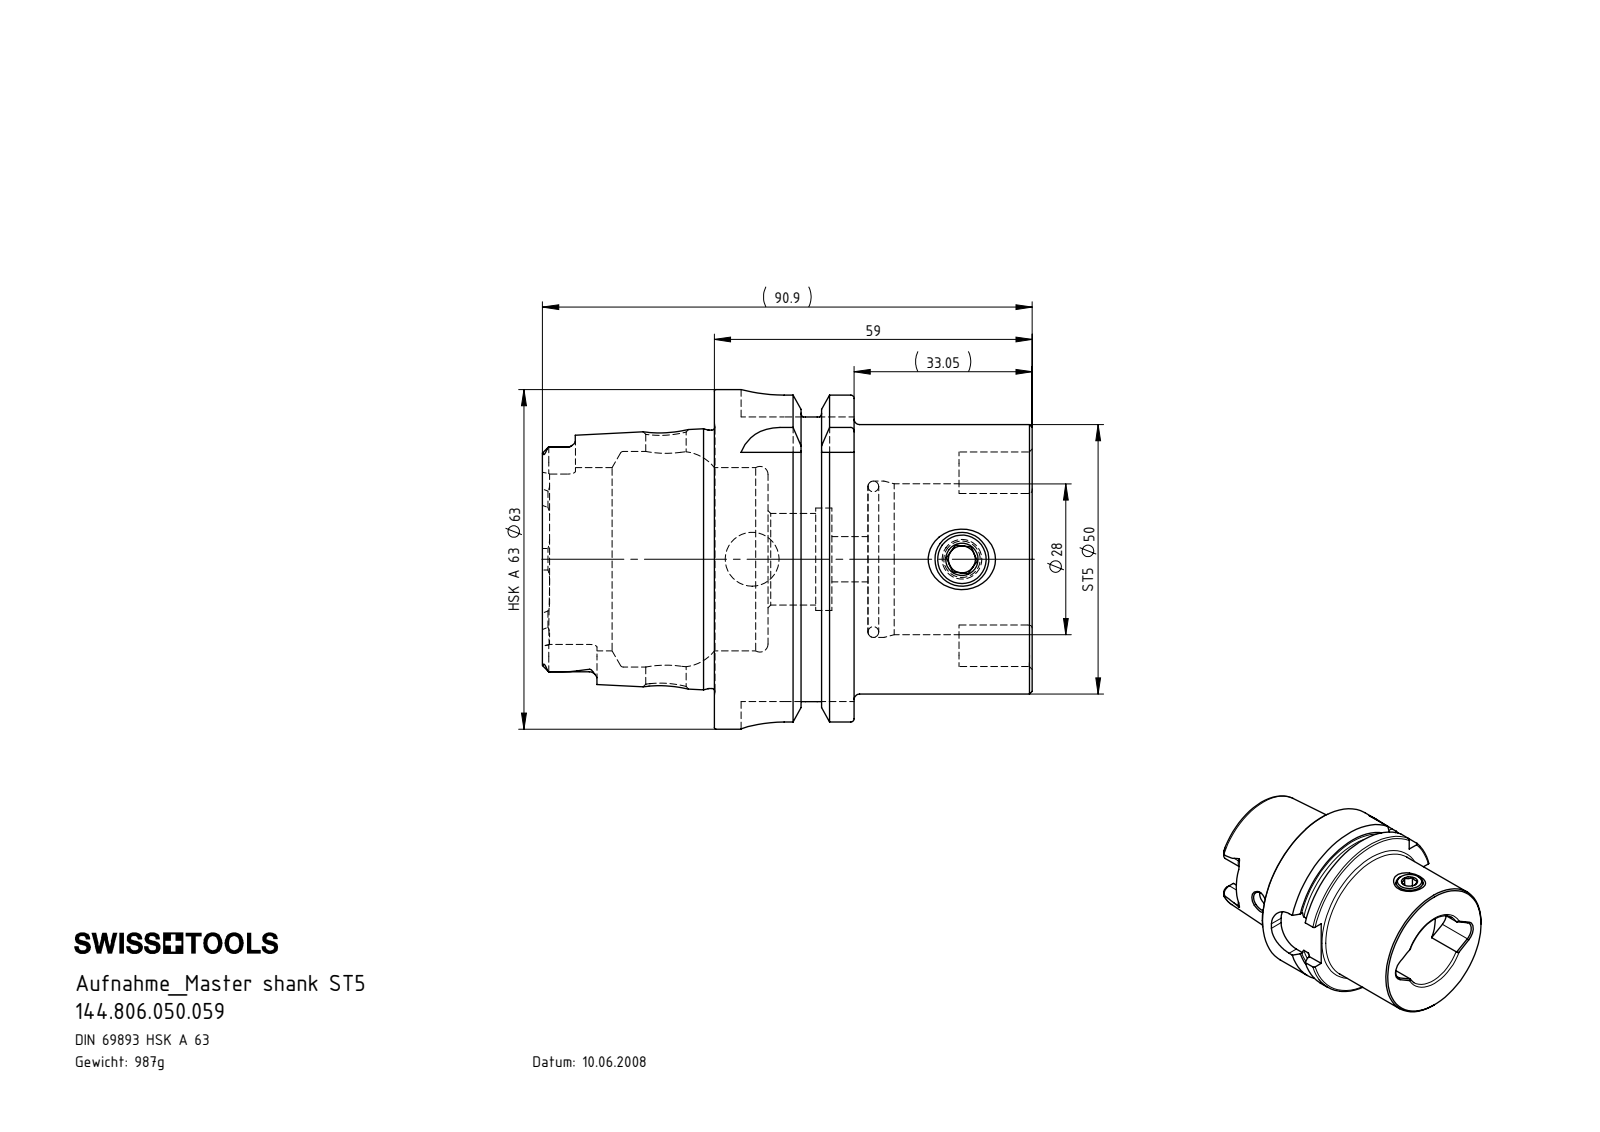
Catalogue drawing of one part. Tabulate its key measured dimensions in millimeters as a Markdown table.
| quantity | value |
| --- | --- |
| part name | ST5-ER1.001.012_A; HA6-ST5.K01.059_B_Fertigbearbeitung; DIN 3771 - 25x2; 144.806.050.059 |
| STEP written by | SolidWorks 2017 (CONFIG_CONTROL_DESIGN) |
| units | millimeters |
| bodies | 3 solids, 227 faces (69 planar, 58 cylindrical, 100 other) |
| overall size | 90.9 × 63 × 63 |
| volume | 125 950 mm³ |
| surface area | 31 593 mm² |
| round holes (diameter × count) | 5 × 1, 7.5 × 1, 8.4 × 1, 9 × 1, 10 × 1, 17 × 1, 19 × 1, 28 × 1, 29 × 1, 34 × 1, 40 × 1 |
| round bosses / shafts (diameter × count) | 63 × 1, 54.95 × 1, 50 × 1, 47.94 × 1, 10 × 1 |
| partial cylindrical surfaces (radius × count) | 1.4 × 6, 2.88 × 4, 8 × 4, 4.2 × 2 |
| main face-to-face distances | 59, 25.95, 33.05, 16, 9.95, 49.05, 28.5, 18.55, 2.55, 30.5 |
| hole center spacings | 38.95 |
